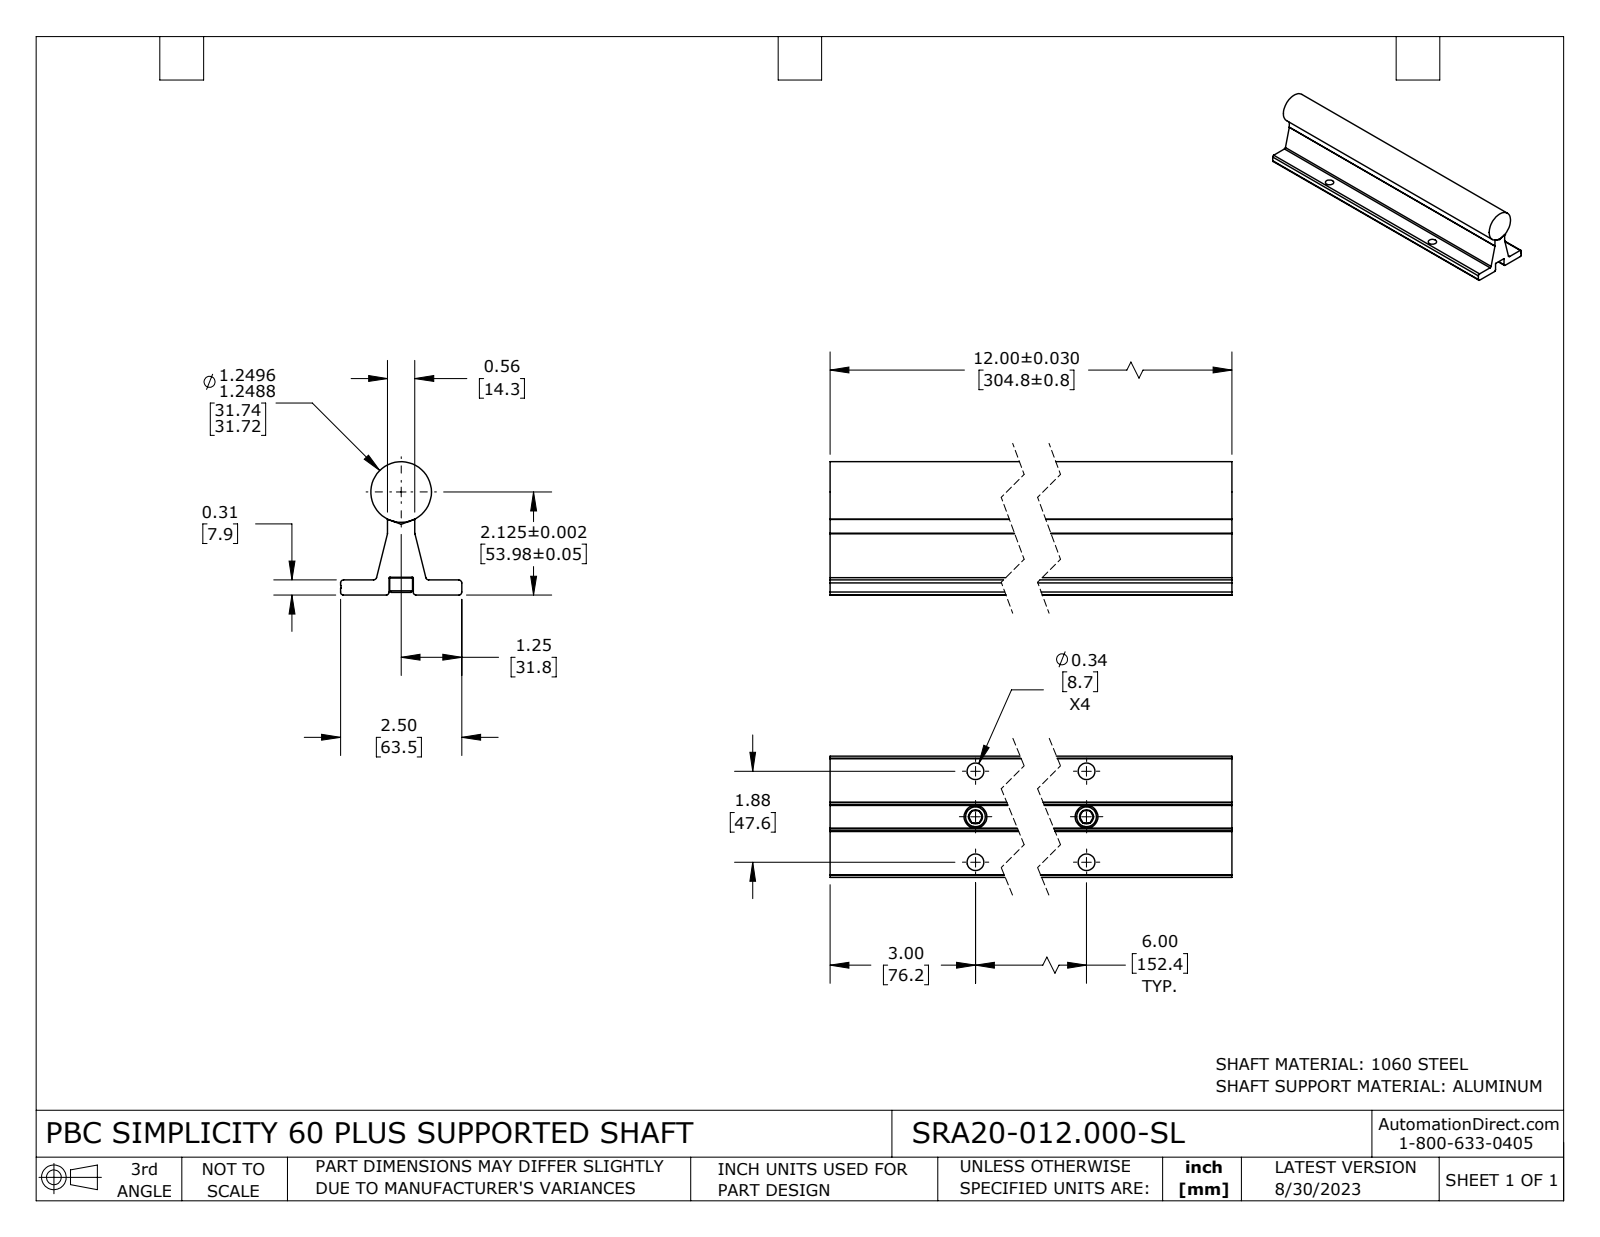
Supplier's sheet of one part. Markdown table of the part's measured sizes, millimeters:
| quantity | value |
| --- | --- |
| part name | SRA20-012.000-SL |
| STEP written by | SolidWorks 2021 (CONFIG_CONTROL_DESIGN) |
| units | millimeters |
| bodies | 4 solids, 123 faces (49 planar, 44 cylindrical, 30 other) |
| overall size | 304.8 × 69.9 × 63.5 |
| volume | 533 900 mm³ |
| surface area | 104 200 mm² |
| round holes (diameter × count) | 8.7 × 6, 6.9 × 2, 9.5 × 2 |
| round bosses / shafts (diameter × count) | 11.9 × 2, 8 × 2, 31.8 × 1 |
| partial cylindrical surfaces (radius × count) | 1.6 × 6, 1.6 × 3, 0.4 × 2, 0.8 × 2, 1.6 × 1 |
| main face-to-face distances | 8, 0.8, 13.5, 9.3, 1.4, 24.6, 25.4, 38.1, 38.9, 12.7 |
| hole center spacings | 23.8, 154.3, 152.4, 47.6, 159.7 |
